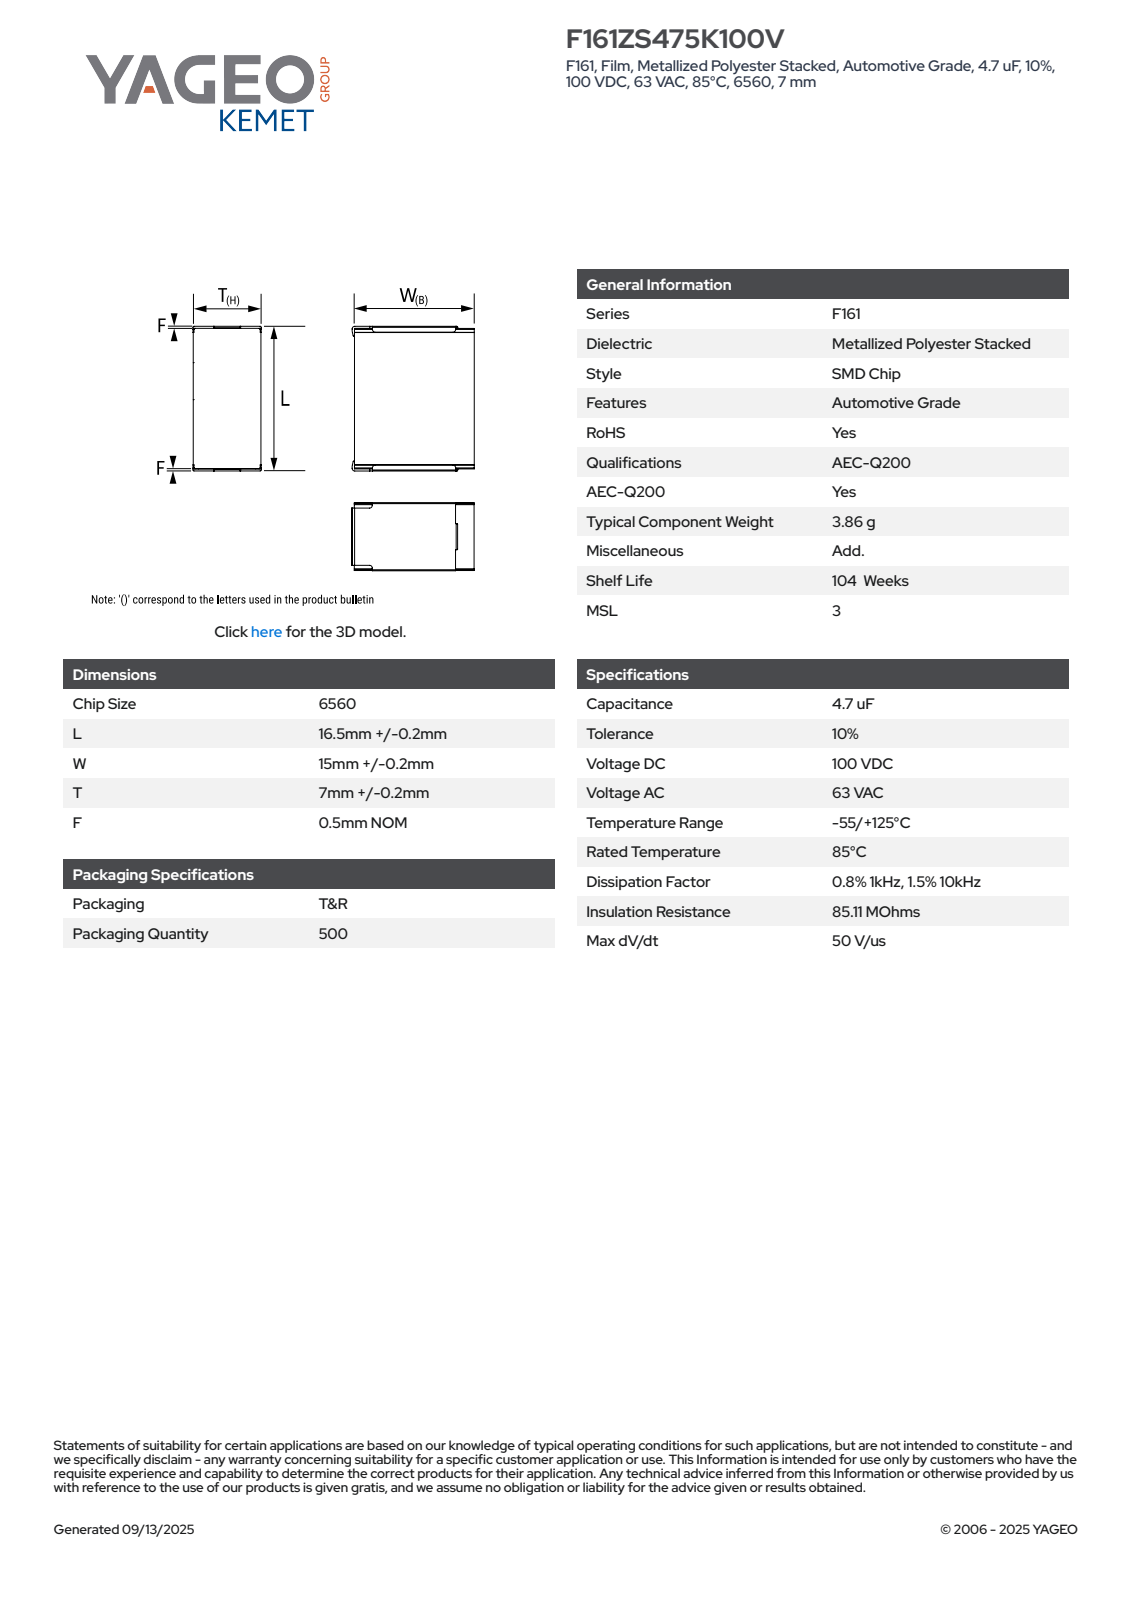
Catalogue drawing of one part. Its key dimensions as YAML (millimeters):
part_name: "CFS_KSTD_6560_L16.7W15.2T7.2F0.5"
step_written_by: "SolidWorks 2021 (AUTOMOTIVE_DESIGN)"
units: millimeters
bodies: {solids: 4, faces: 117, planar: 103, cylindrical: 14, other: 0}
overall_size: [16.7, 15.71, 7.57]
volume: 1779
surface_area: 1027
partial_cylinders:
  - {radius: 0.43, count: 10}
  - {radius: 0.59, count: 4}
face_to_face_distances: [7.2, 16.7, 14.59, 0.5, 16.2, 7.38, 0.61, 15.7, 7.56, 15.2]
